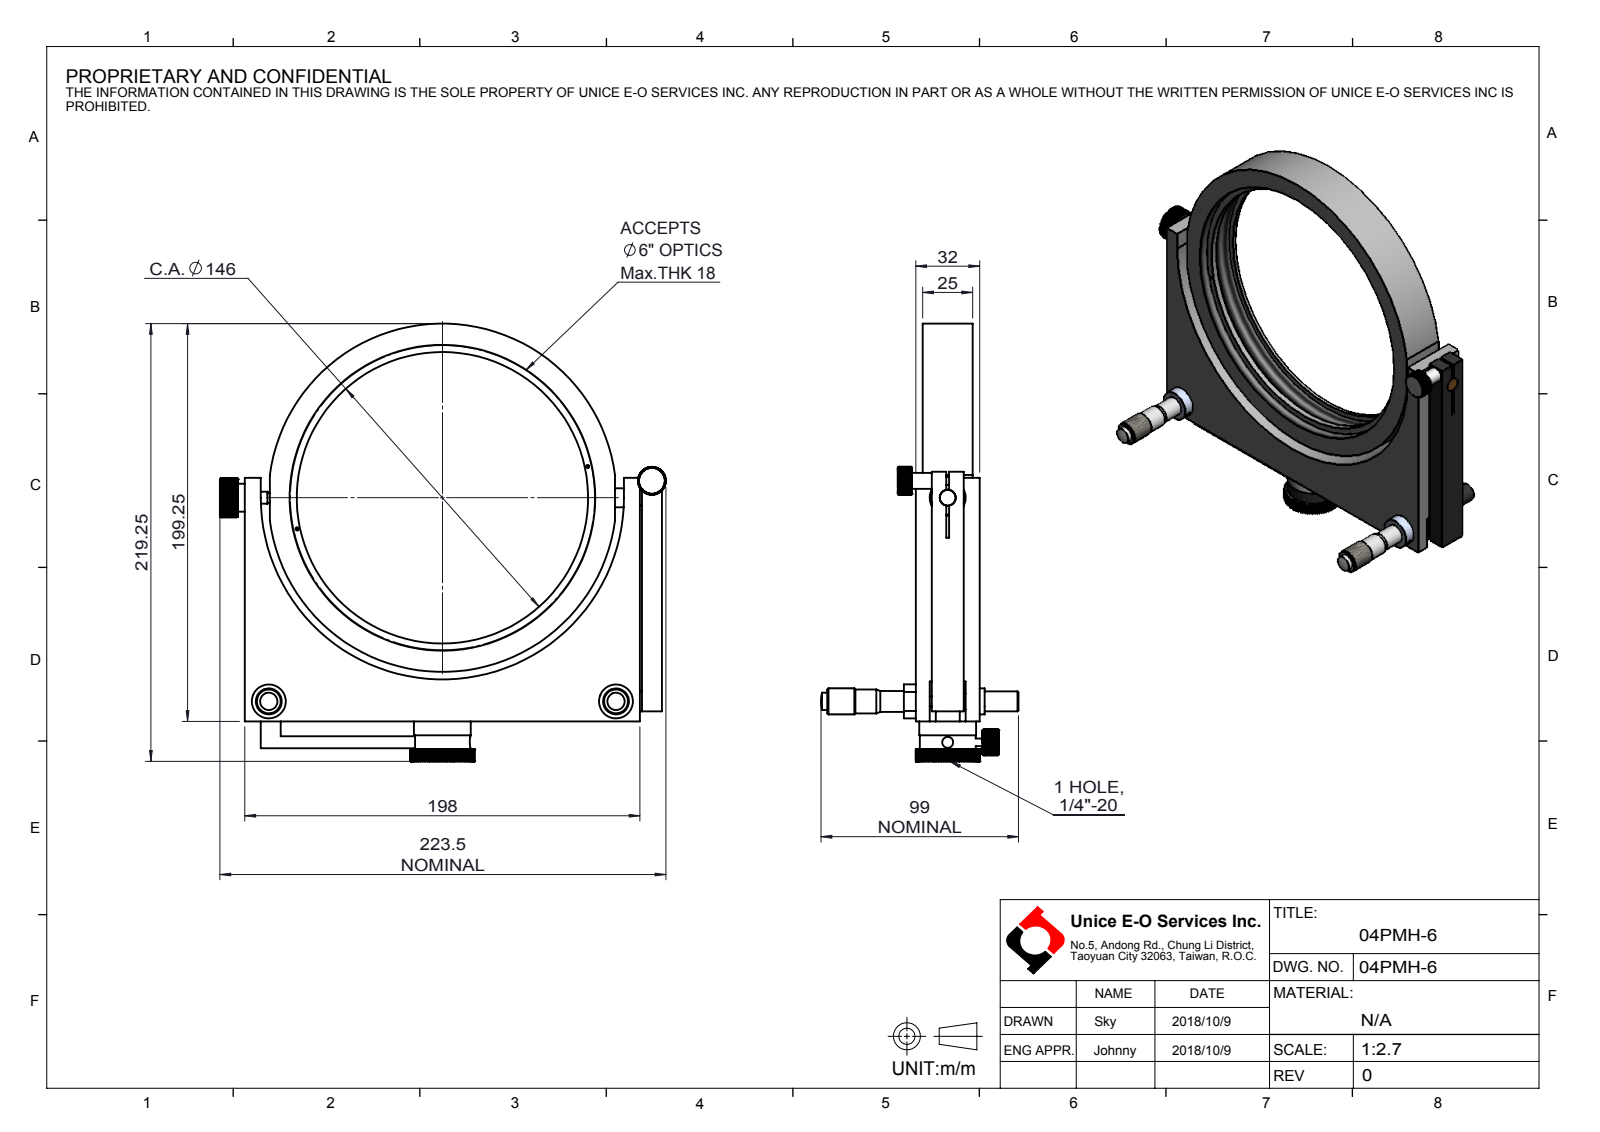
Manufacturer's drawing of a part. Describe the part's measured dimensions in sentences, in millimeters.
The part is named "04PMH-6". Its 3-D file was written by "SolidWorks 2016 (AUTOMOTIVE_DESIGN)". It is 0 solids with 1020 faces: 499 planar, 301 cylindrical and 220 other. Overall it measures 223.5 by 219.25 by 99 millimeters. Round holes: 2 of diameter 1.5, 2 of diameter 2.5, 2 of diameter 9.5, 2 of diameter 12, 1 of diameter 5.11, 1 of diameter 5.5, 1 of diameter 8.5, 1 of diameter 11, 1 of diameter 146, 1 of diameter 147, 1 of diameter 149, 1 of diameter 153.2. Round bosses or shafts: 4 of diameter 8, 3 of diameter 17, 2 of diameter 13, 2 of diameter 10.5, 2 of diameter 10, 2 of diameter 8.7, 2 of diameter 5, 1 of diameter 174.5. Partial cylindrical surfaces (rounded edges, fillets, slot ends): 4 of radius 3, 1 of radius 6.5, 1 of radius 7, 1 of radius 9.75, 1 of radius 16, 1 of radius 91. The main face-to-face distances are 3.5, 28.5, 32, 25, 198, 1, 19.4, 9.1, 8, 11. The hole center spacings are 134.06, 66.27, 74.5, 74.51, 87.53, 118.48, 122.5, 149.
